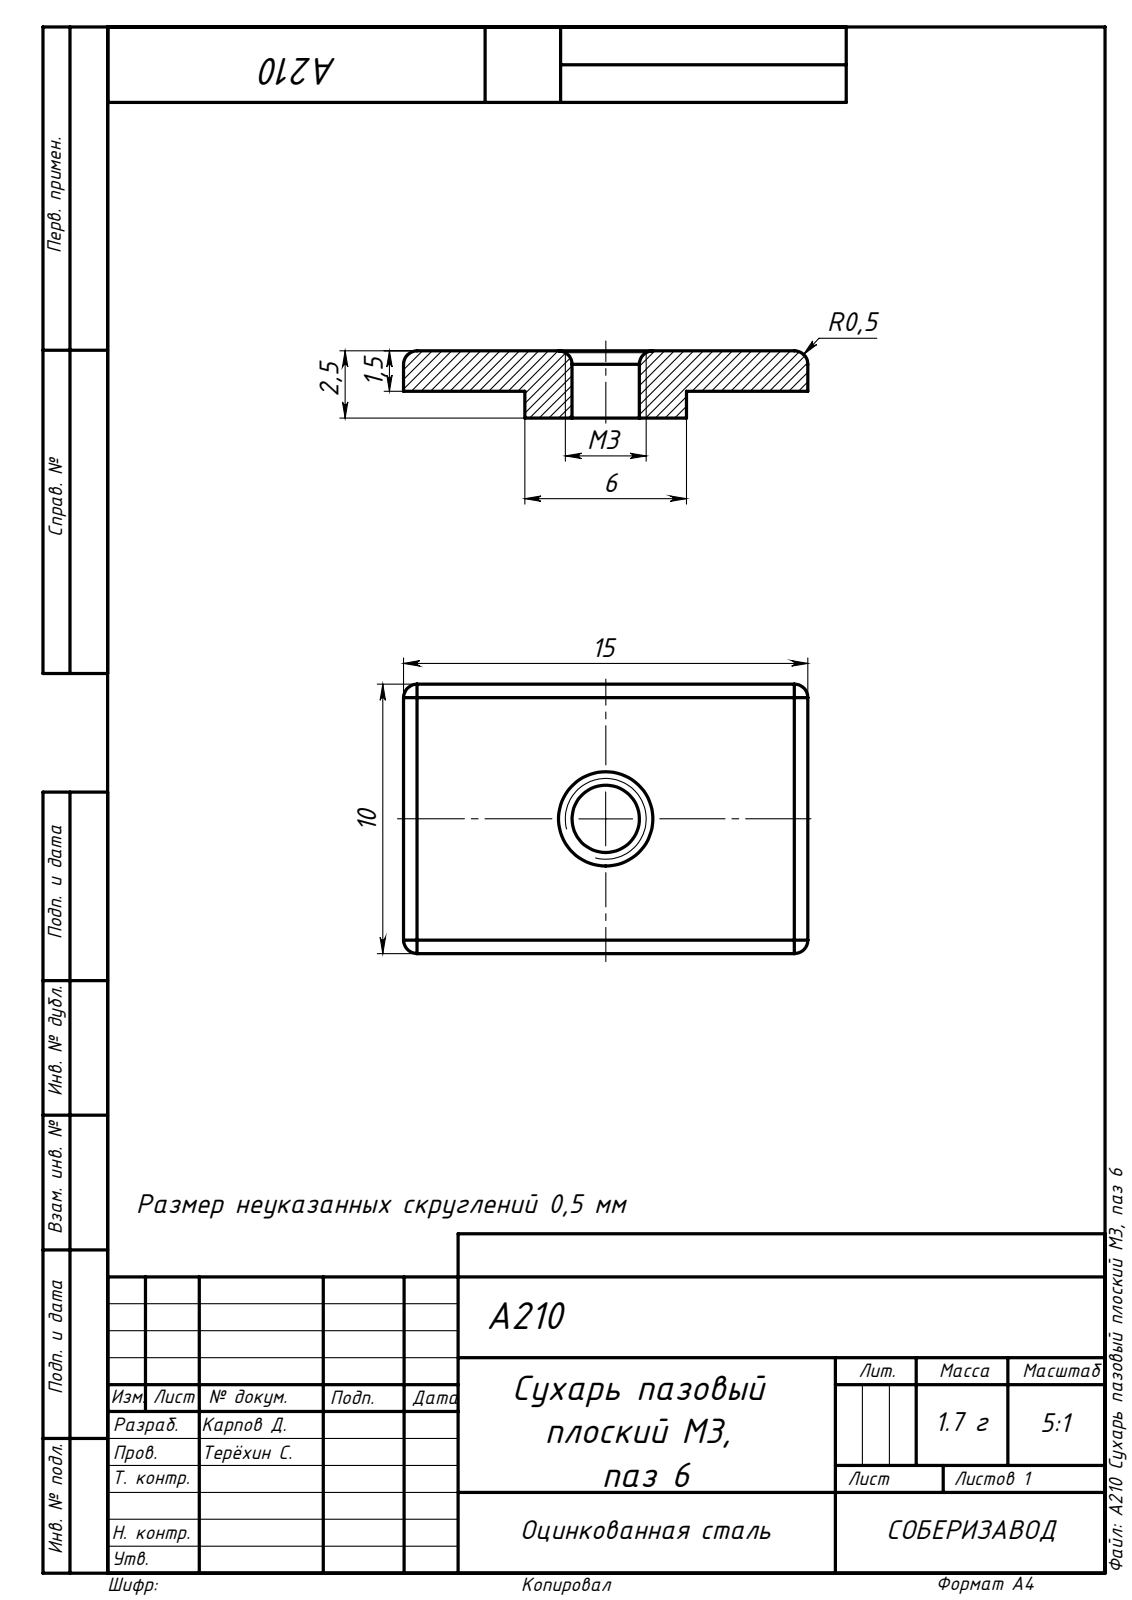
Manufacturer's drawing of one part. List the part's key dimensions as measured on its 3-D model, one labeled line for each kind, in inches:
Part name (STEP PRODUCT): A210 Сухарь пазовый плоский M3, паз 6
STEP written by: SolidWorks 2019 (AUTOMOTIVE_DESIGN)
Units: inches
Bodies: 1 solid, 25 faces (7 planar, 12 cylindrical, 6 other)
Overall size (bounding box): 0.591 × 0.394 × 0.098
Volume: 0.015 in³ · Surface area: 0.605 in²
Round holes (diameter × count): ⌀0.098 ×1
Round bosses / shafts (diameter × count): ⌀0.236 ×1
Partial cylindrical surfaces — rounded edges, fillets, slot ends (radius × count): R0.02 ×8
Main face-to-face distances: 0.059, 0.039, 0.098, 0.394, 0.591
